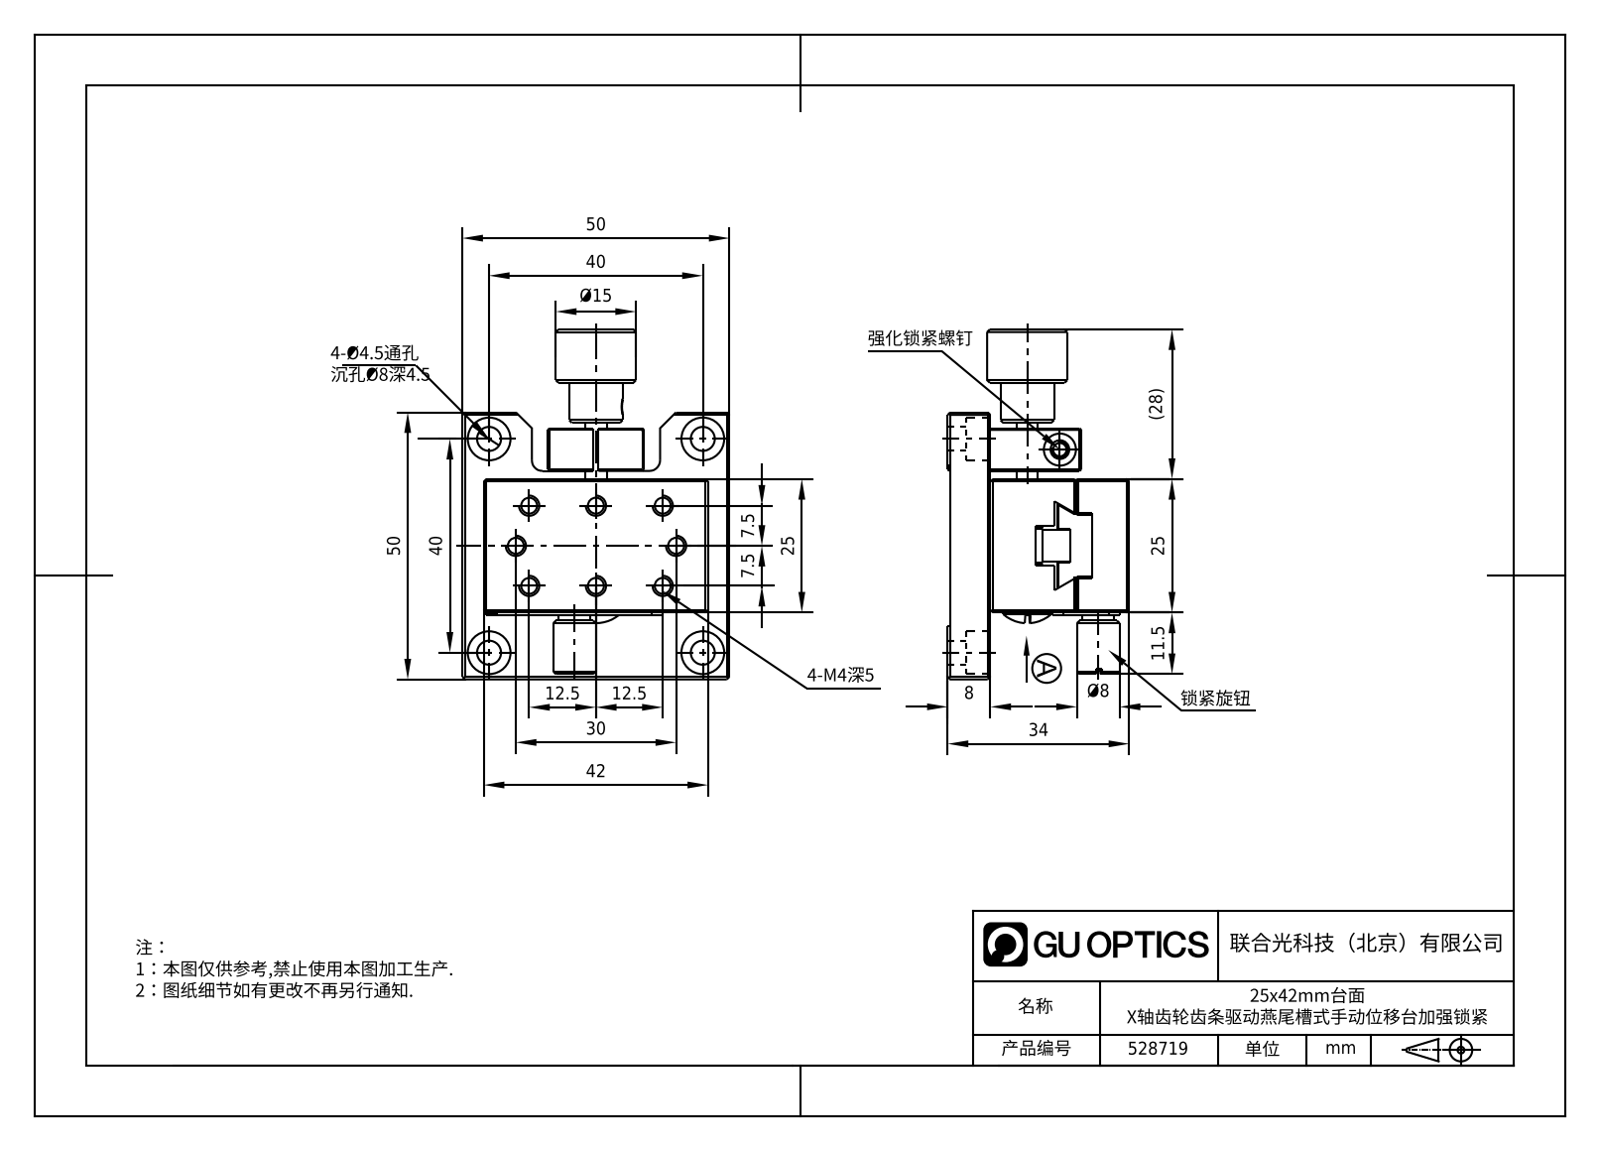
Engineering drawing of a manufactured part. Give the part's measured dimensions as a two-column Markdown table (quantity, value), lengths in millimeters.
| quantity | value |
| --- | --- |
| part name | 528719 |
| STEP written by | SolidWorks 2020 (CONFIG_CONTROL_DESIGN) |
| units | millimeters |
| bodies | 6 solids, 548 faces (310 planar, 72 cylindrical, 166 other) |
| overall size | 65.51 × 50 × 34 |
| volume | 46 912 mm³ |
| surface area | 24 562 mm² |
| round holes (diameter × count) | 3.24 × 10, 4.5 × 6, 2.01 × 4, 2.46 × 4, 6 × 4, 8 × 4, 3.5 × 3, 1.57 × 2, 2.2 × 2, 2.6 × 2, 2.8 × 2, 4 × 2 |
| round bosses / shafts (diameter × count) | 8 × 2, 9 × 1, 6.5 × 1, 6 × 1, 5.83 × 1, 4 × 1, 3 × 1 |
| partial cylindrical surfaces (radius × count) | 2 × 6, 1.8 × 2 |
| main face-to-face distances | 7.5, 16, 19, 26.5, 0.5, 4, 3, 7, 8, 25 |
| hole center spacings | 34, 23.58, 28.5, 7.65, 7.91, 8.75, 9.01, 10.61 |
